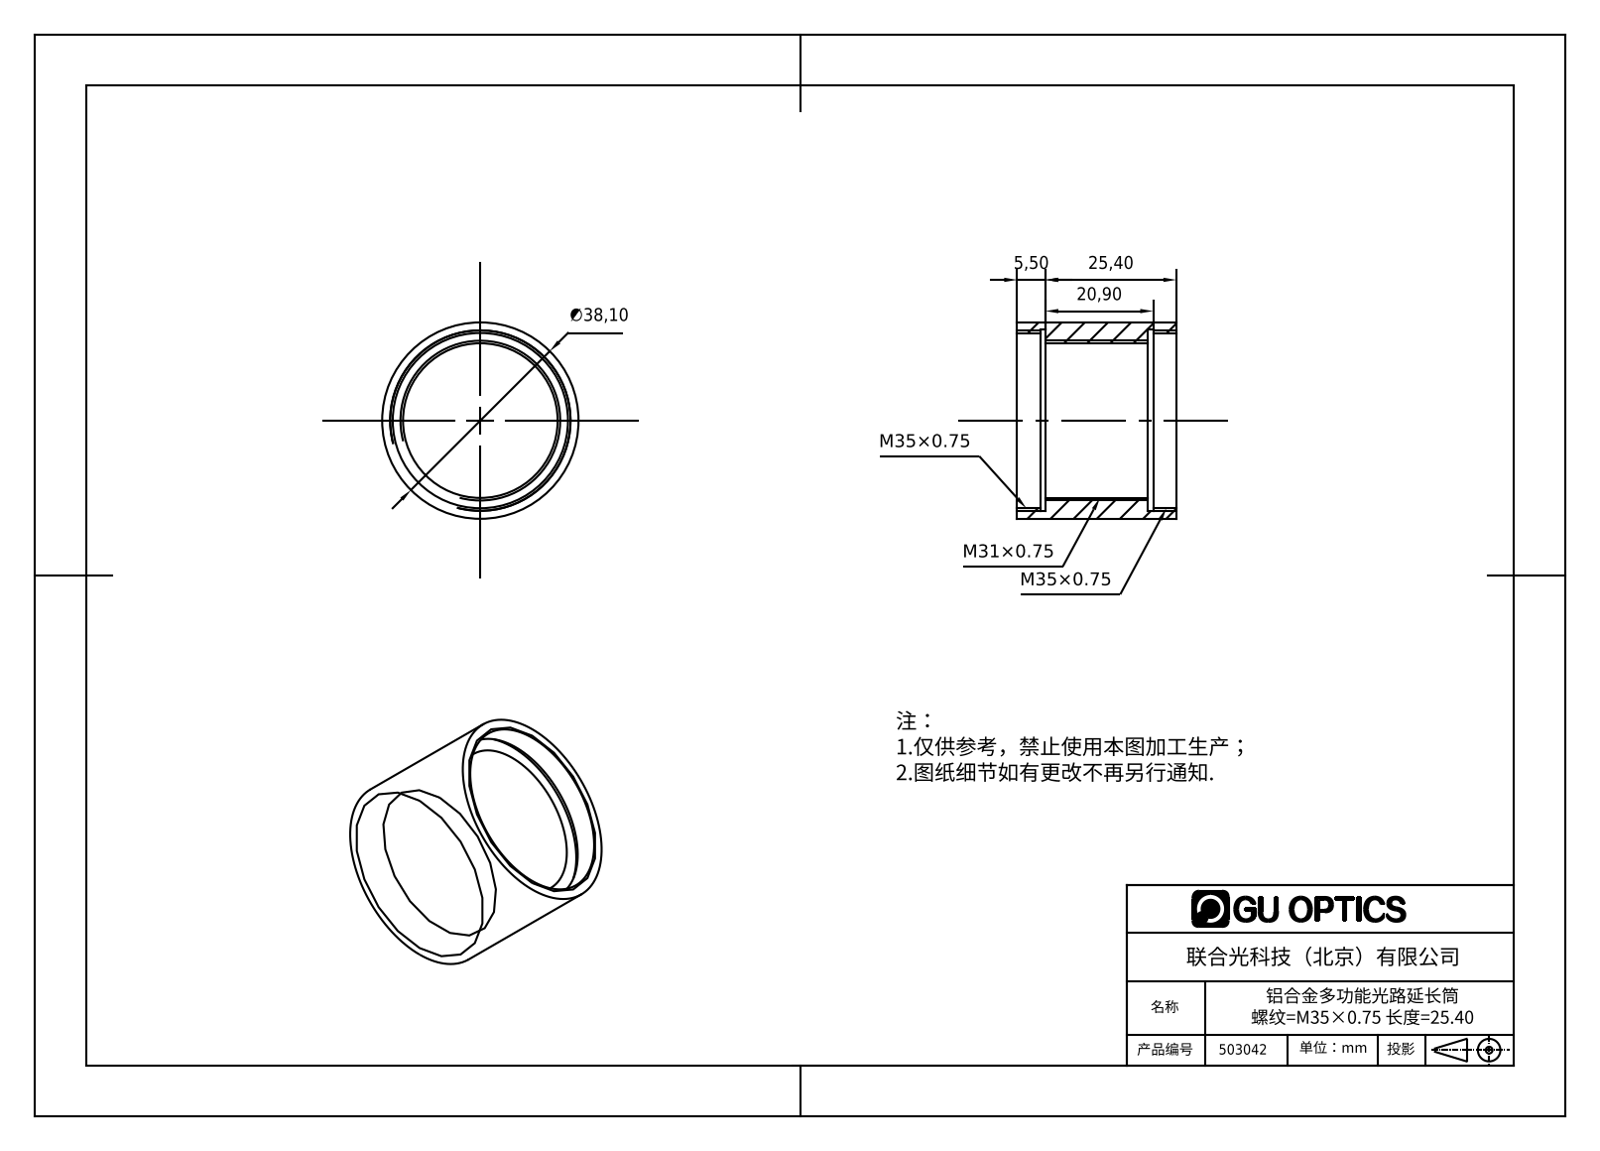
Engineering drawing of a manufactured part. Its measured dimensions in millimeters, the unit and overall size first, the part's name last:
Units: millimetres
Overall size (bounding box): 38.1 × 38.1 × 30.9
Round holes (diameter × count): ⌀30 ×1, ⌀34 ×1, ⌀35.2 ×1
Round bosses / shafts (diameter × count): ⌀38.1 ×1
Main face-to-face distances: 5.5, 25.4, 19.9, 30.9, 4.5, 26.4, 1, 20.9, 21.9
Volume: 11 045 mm³ · Surface area: 7 884 mm²
Bodies: 1 solid, 18 faces (6 planar, 12 cylindrical, 0 other)
Part name (STEP PRODUCT): 503042
STEP written by: SolidWorks 2016 (AUTOMOTIVE_DESIGN)
